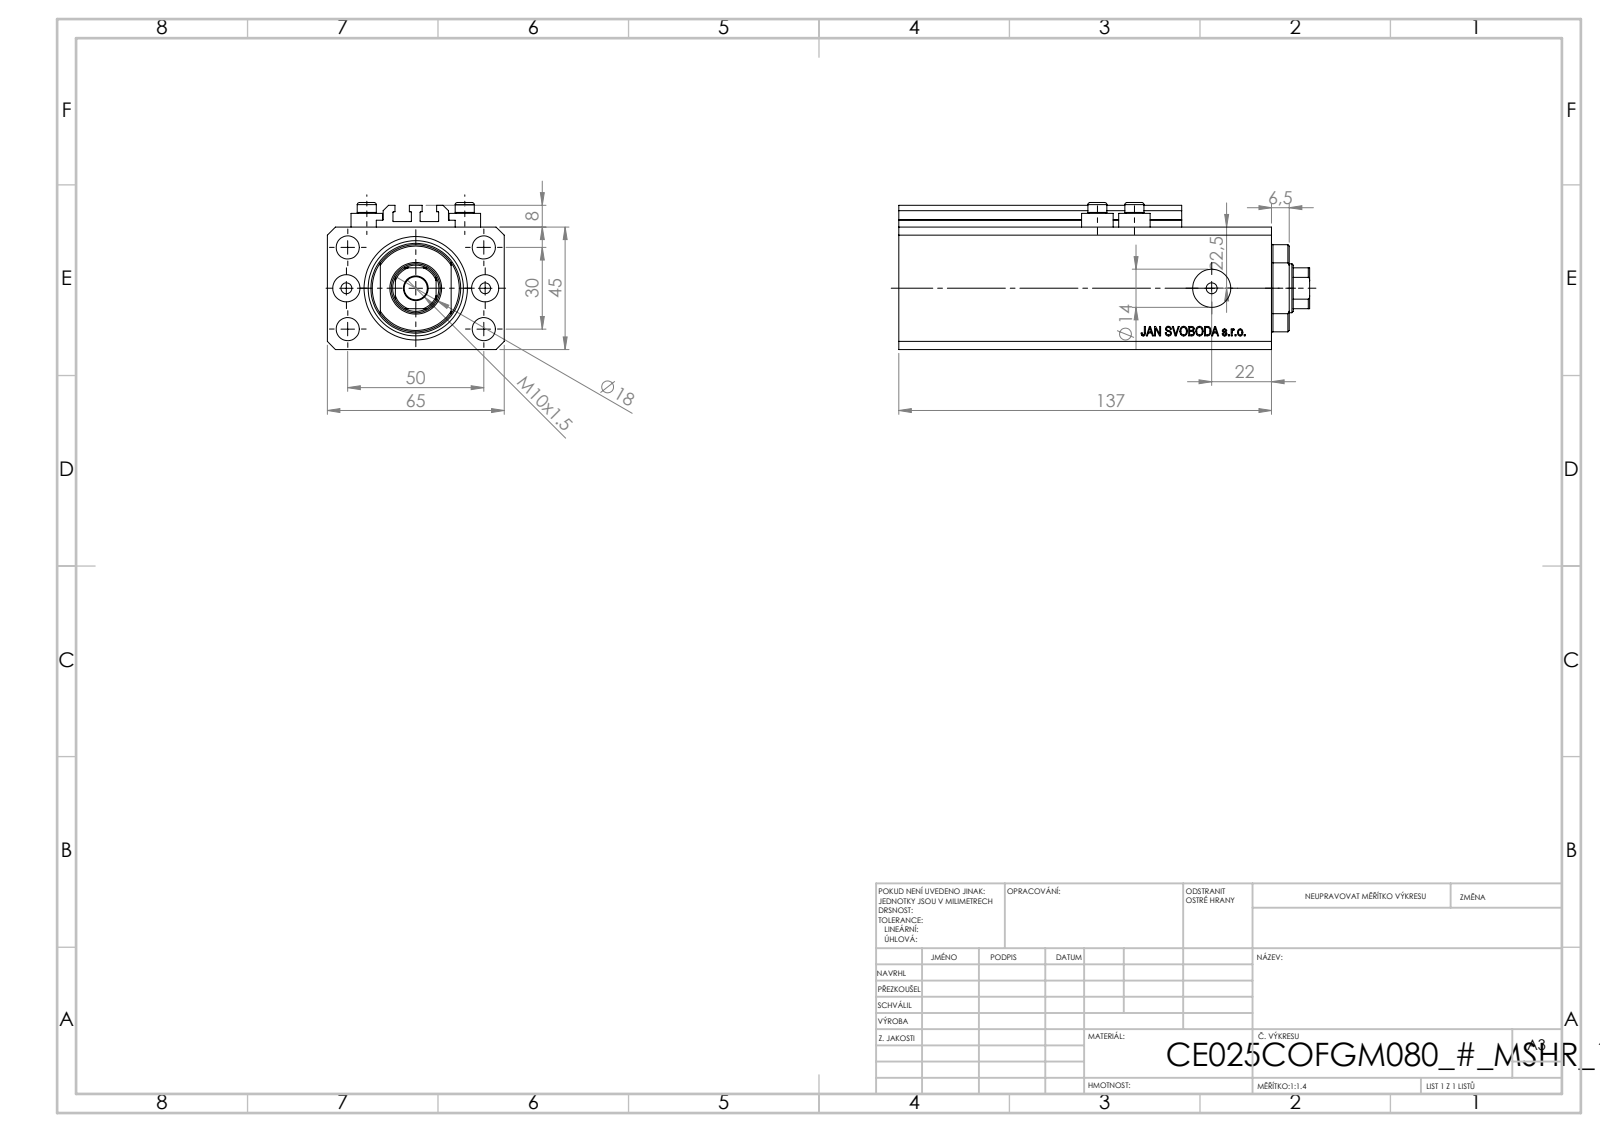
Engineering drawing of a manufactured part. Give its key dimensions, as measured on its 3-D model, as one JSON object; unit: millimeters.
{"part_name": "V250CE_C_Body; V250CE_C_VCP; ALLEN BOLT V250CE; V250CE_VC_C", "step_written_by": "SolidWorks 2019 (CONFIG_CONTROL_DESIGN)", "units": "millimeters", "bodies": {"solids": 8, "faces": 1033, "planar": 503, "cylindrical": 86, "other": 444}, "overall_size": [150.9, 65, 54], "volume_mm3": 366076, "surface_area_mm2": 92764, "round_holes": [[4, 8], [8.5, 5], [10, 2], [14, 2], [18, 1], [25, 1], [38, 1]], "round_bosses_or_shafts": [[11.6, 4], [7, 4]], "partial_cylinders_radius": [[0.2, 10], [8.5, 1], [16, 1]], "face_to_face_distances": [45, 65, 47, 111.9, 137, 25.1, 2.5, 2, 10, 73.52], "hole_center_spacings": [15.01, 29.15, 52.68, 13.6, 25.5, 30, 36, 38.48]}
